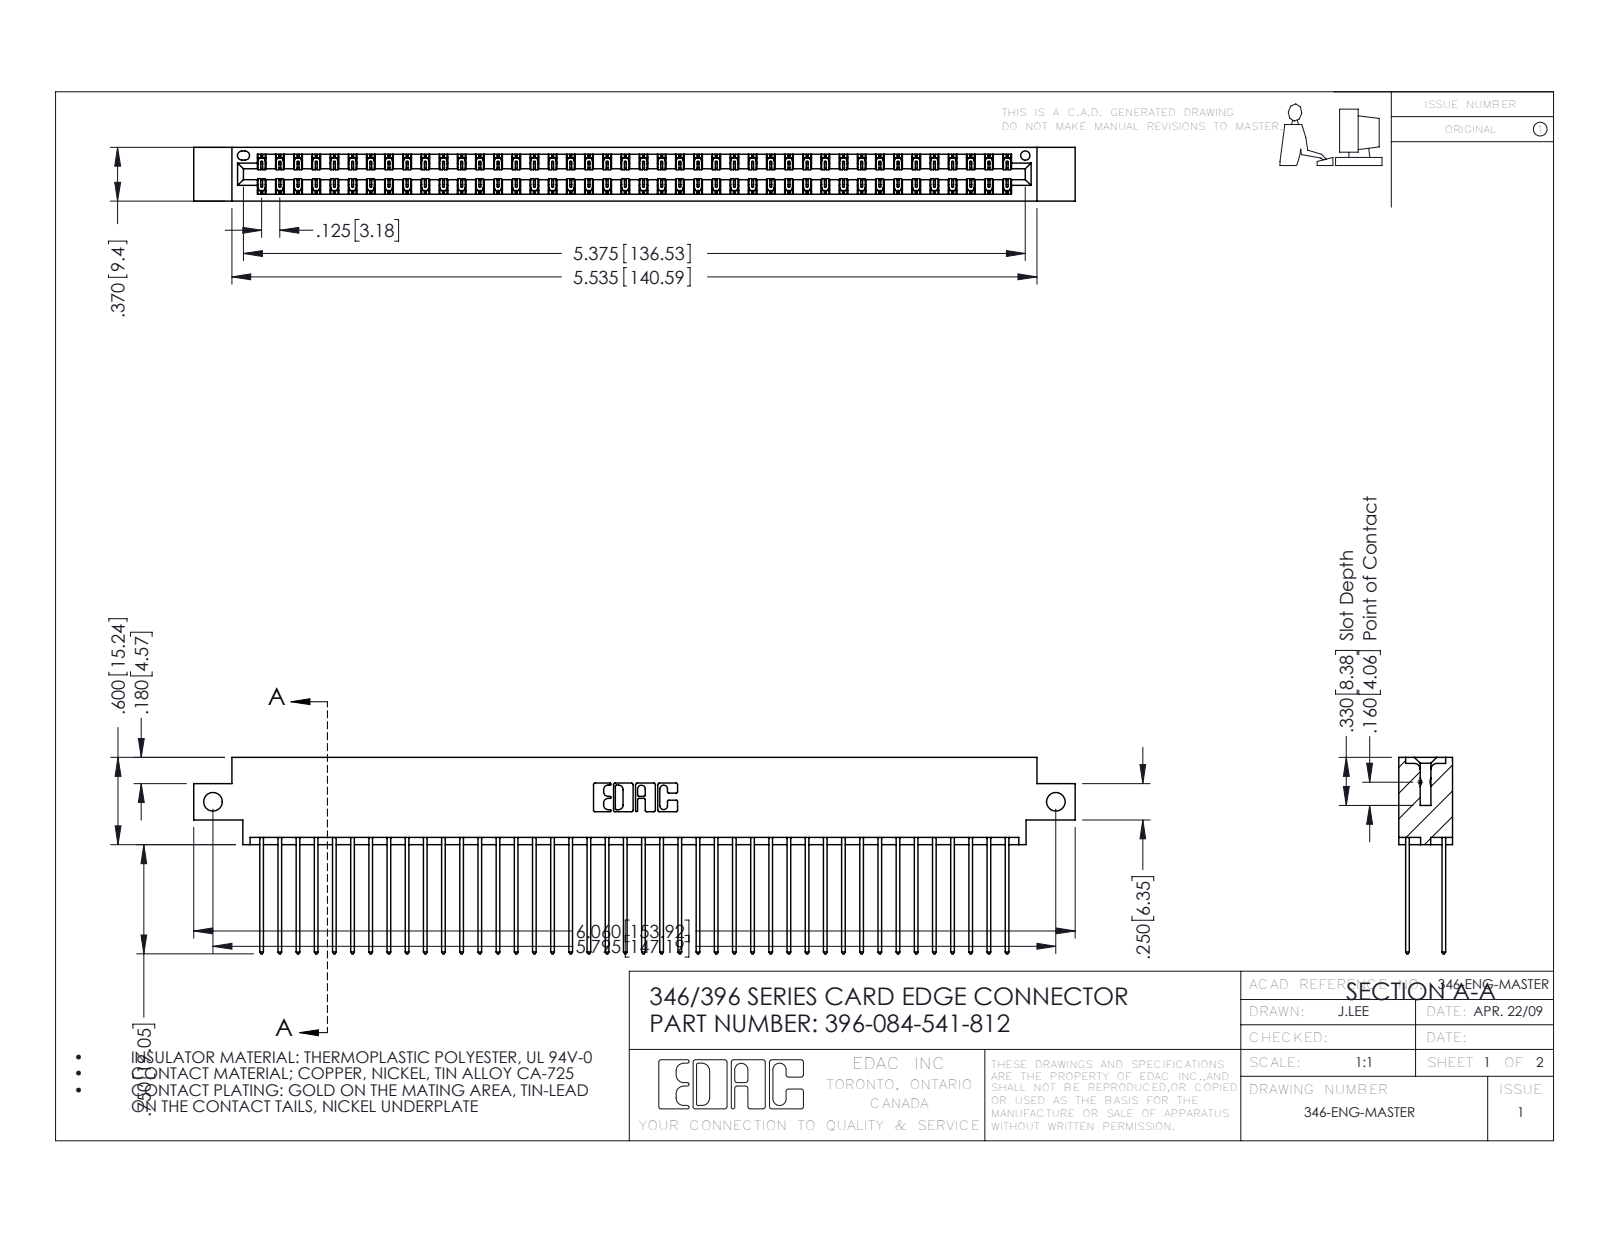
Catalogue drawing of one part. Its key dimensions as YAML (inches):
part_name: "345-292-001_345-293-141; 346 Part_0.170 Offset - Side Mount; 396-084-541-812"
step_written_by: "SolidWorks 2016 (CONFIG_CONTROL_DESIGN)"
units: inches
bodies: {solids: 85, faces: 4494, planar: 3020, cylindrical: 1474, other: 0}
overall_size: [6.06, 1.35, 0.37]
volume: 0.931
surface_area: 36.14
round_holes:
  - {diameter: 0.128, count: 2}
  - {diameter: 0.064, count: 1}
partial_cylinders:
  - {radius: 0.006, count: 126}
  - {radius: 0.01, count: 84}
  - {radius: 0.01, count: 22}
  - {radius: 0.007, count: 6}
  - {radius: 0.031, count: 6}
  - {radius: 0.026, count: 3}
  - {radius: 0.014, count: 2}
  - {radius: 0.022, count: 2}
face_to_face_distances: [0.048, 0.322, 0.25, 0.072, 0.298, 0.025, 0.37, 0.275, 0.225, 0.148]
hole_center_spacings: [5.795]
